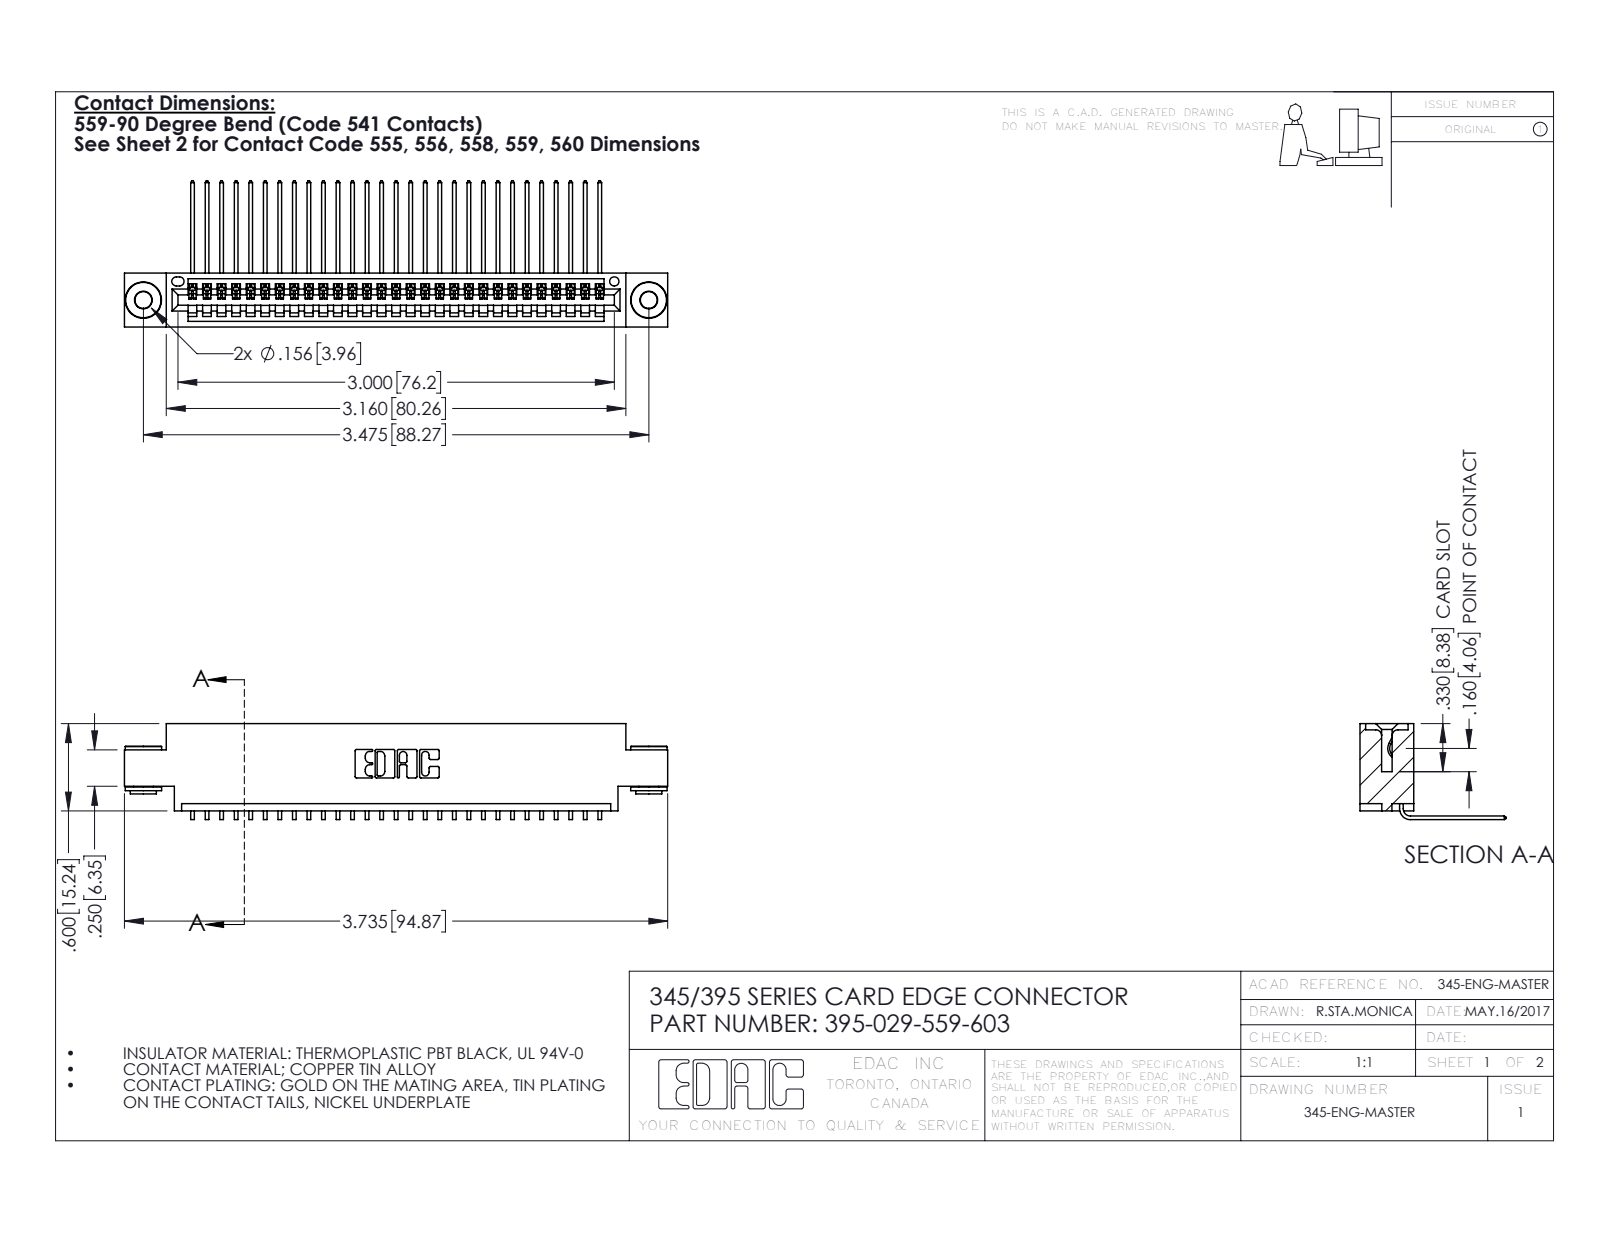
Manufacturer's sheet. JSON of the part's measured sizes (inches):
{"part_name": "395-029-559-603; 345-250-002_345-250-002-102; 345-292-001_558 559 Tail - 1; 345 Part_0.170 Offset - 0.156 Dia-TH", "step_written_by": "SolidWorks 2016 (CONFIG_CONTROL_DESIGN)", "units": "inches", "bodies": {"solids": 32, "faces": 1908, "planar": 1312, "cylindrical": 588, "other": 8}, "overall_size": [3.735, 1.005, 0.659], "volume_in3": 0.544, "surface_area_in2": 19.48, "round_holes": [[0.116, 2], [0.156, 2], [0.064, 1]], "round_bosses_or_shafts": [[0.25, 2], [0.18, 2], [0.136, 2]], "partial_cylinders_radius": [[0.006, 58], [0.01, 22], [0.007, 6], [0.031, 6], [0.026, 3], [0.031, 2], [0.04, 2], [0.014, 1]], "face_to_face_distances": [0.072, 0.298, 0.37, 0.2, 0.098, 0.272, 0.025, 0.225, 0.175, 0.149], "hole_center_spacings": [0.27, 3.24, 3.475]}
